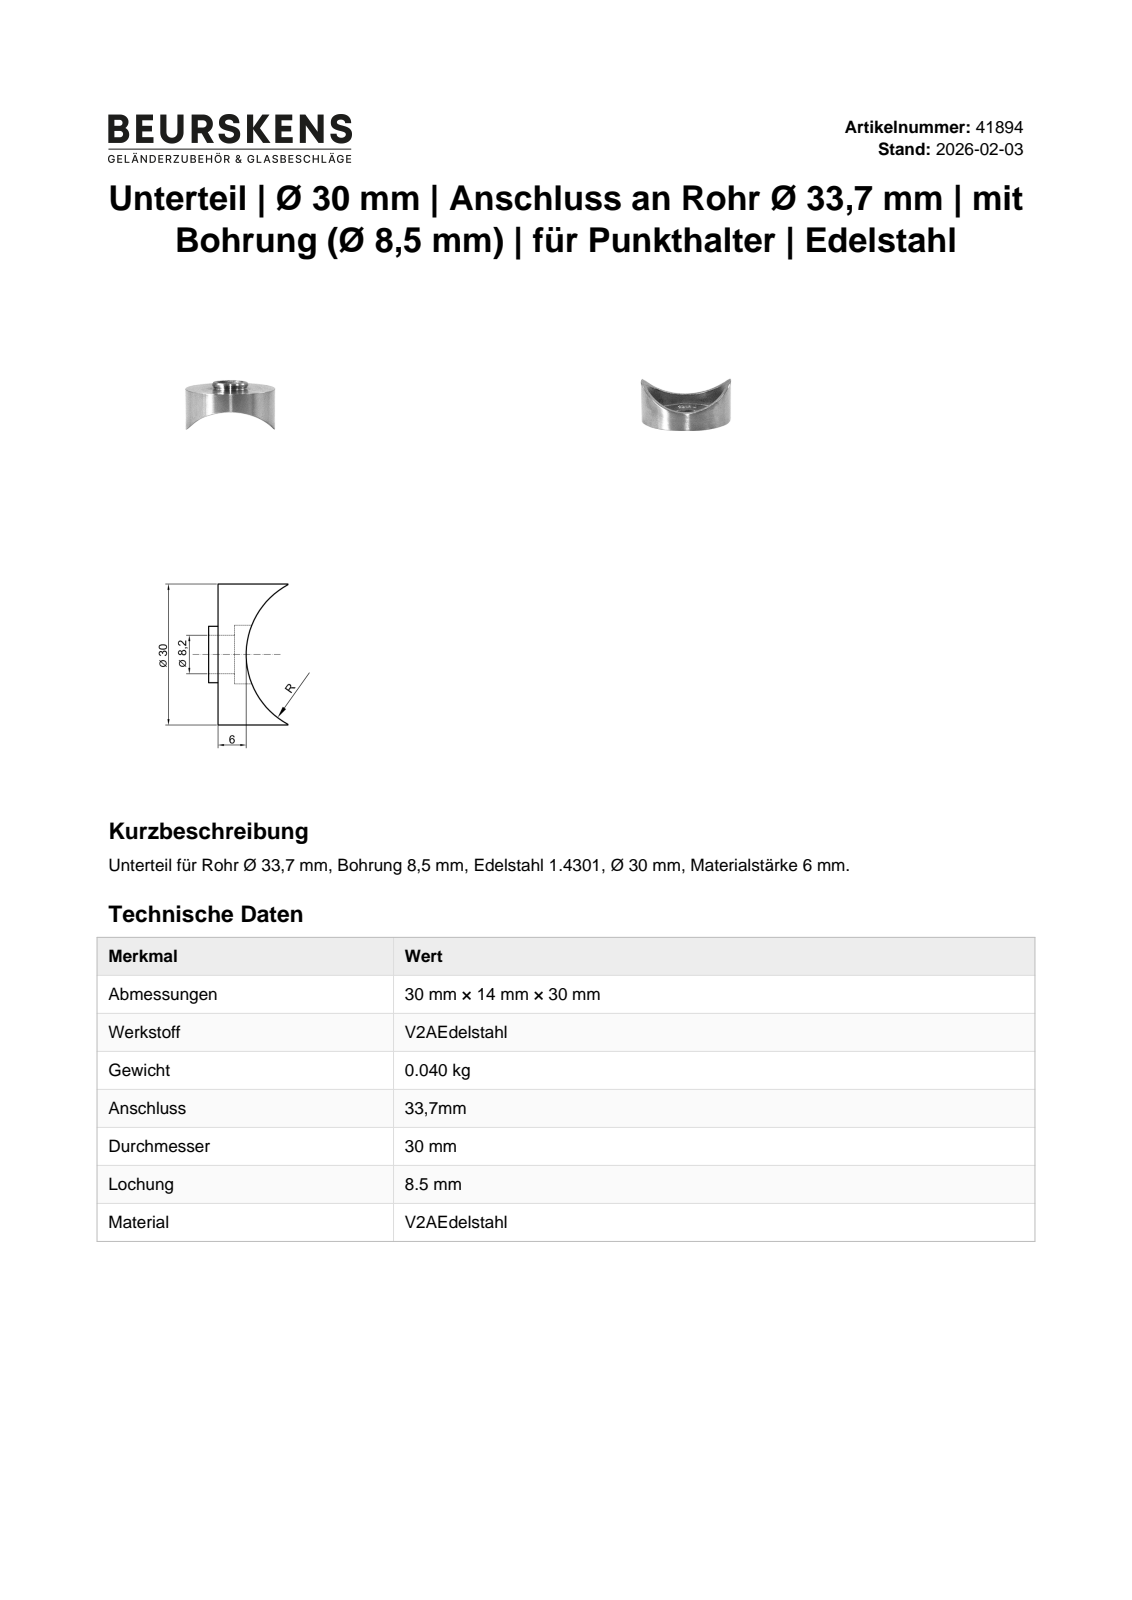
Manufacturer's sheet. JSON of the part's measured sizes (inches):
{"part_name": "41894", "step_written_by": "Autodesk Inventor 2023 (AUTOMOTIVE_DESIGN)", "units": "inches", "bodies": {"solids": 1, "faces": 8, "planar": 3, "cylindrical": 5, "other": 0}, "overall_size": [1.181, 1.181, 0.656], "volume_in3": 0.221, "surface_area_in2": 4.517, "round_holes": [[0.335, 1], [0.945, 1]], "round_bosses_or_shafts": [[1.181, 1], [0.472, 1]], "partial_cylinders_radius": [[0.663, 1]], "face_to_face_distances": [0.118, 0.177, 0.059]}
